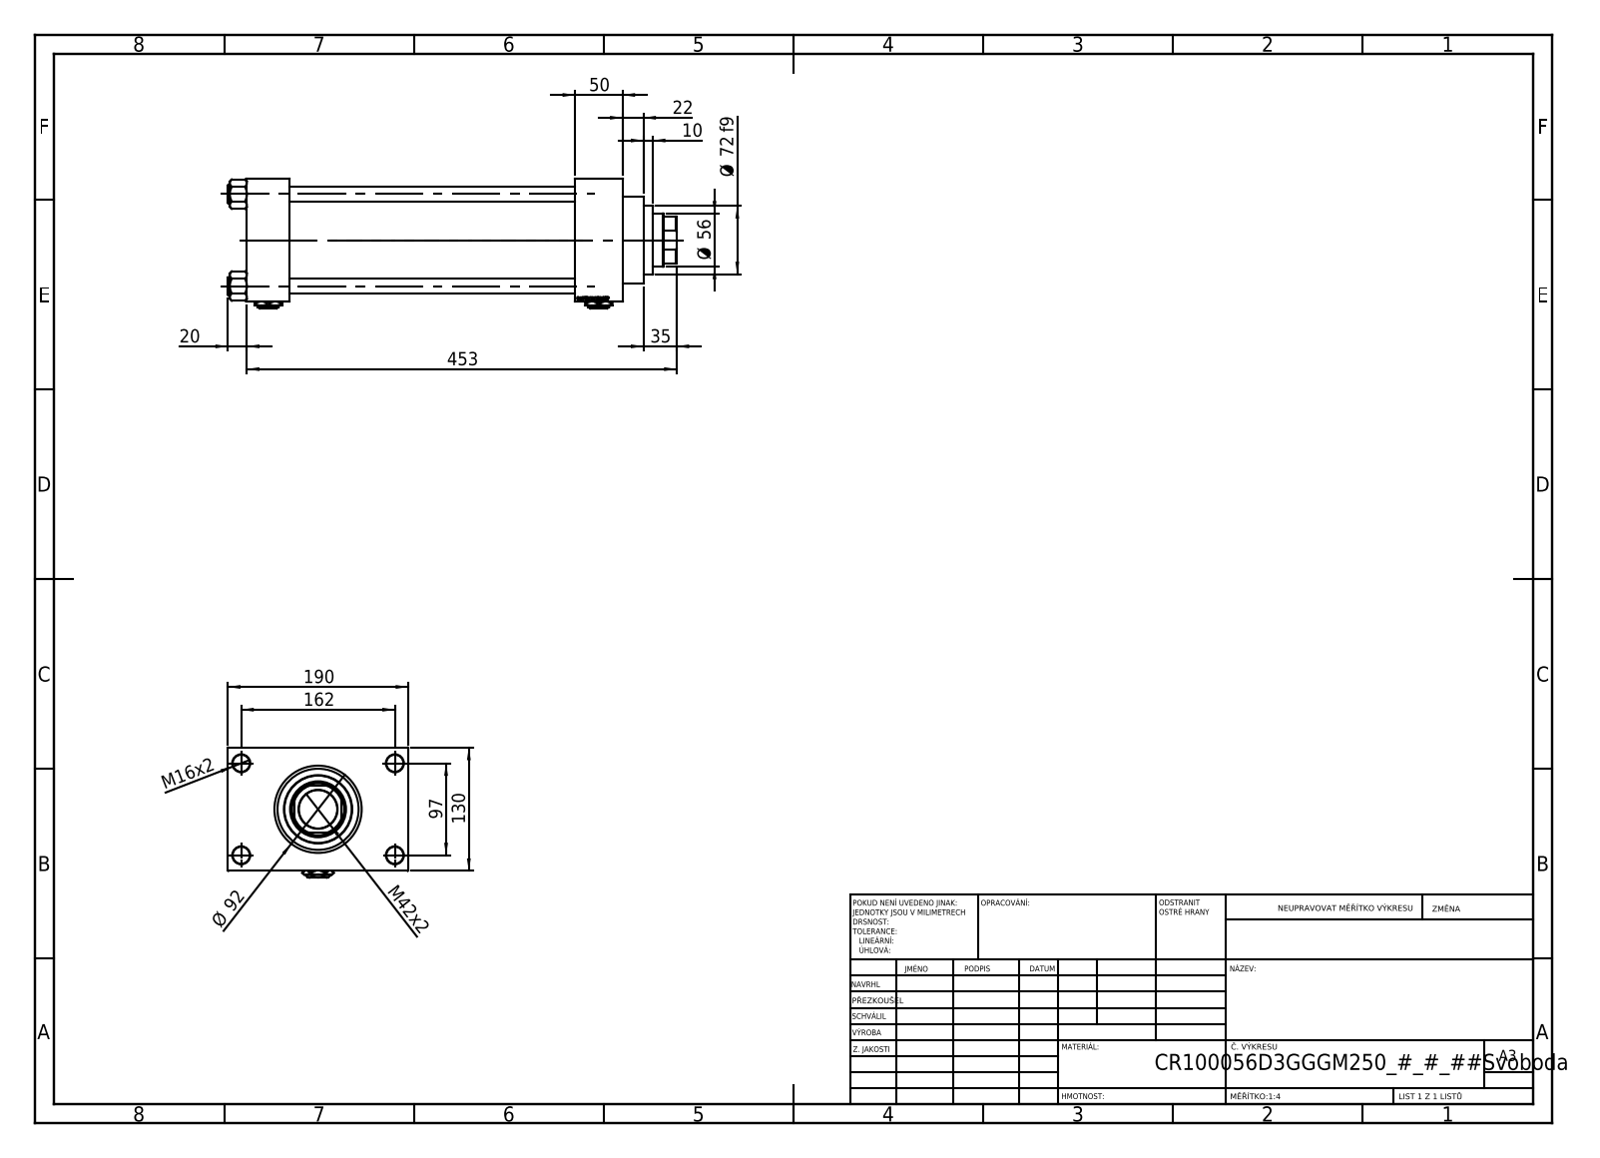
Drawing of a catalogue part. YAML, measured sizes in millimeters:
part_name: "V215CR_VCP_D; NUT_M5_D; V215_VC_A; V215CR_D_Body (+2 more)"
step_written_by: "SolidWorks 2019 (CONFIG_CONTROL_DESIGN)"
units: millimeters
bodies: {solids: 13, faces: 1253, planar: 593, cylindrical: 100, other: 560}
overall_size: [473, 190, 137]
volume: 3605000
surface_area: 602355
round_holes:
  - {diameter: 16, count: 4}
  - {diameter: 18, count: 4}
  - {diameter: 7, count: 2}
  - {diameter: 26.44, count: 2}
  - {diameter: 35, count: 2}
  - {diameter: 40.5, count: 1}
  - {diameter: 56, count: 1}
  - {diameter: 59, count: 1}
  - {diameter: 76, count: 1}
  - {diameter: 85.5, count: 1}
  - {diameter: 100, count: 1}
round_bosses_or_shafts:
  - {diameter: 19, count: 4}
  - {diameter: 106, count: 1}
  - {diameter: 92, count: 1}
  - {diameter: 72, count: 1}
partial_cylinders:
  - {radius: 27, count: 1}
face_to_face_distances: [130, 50, 45, 346, 301, 351, 396, 30, 160, 190]
hole_center_spacings: [32.55, 68.52, 94.41, 96.9, 102.27, 129.45, 161.73, 97]
